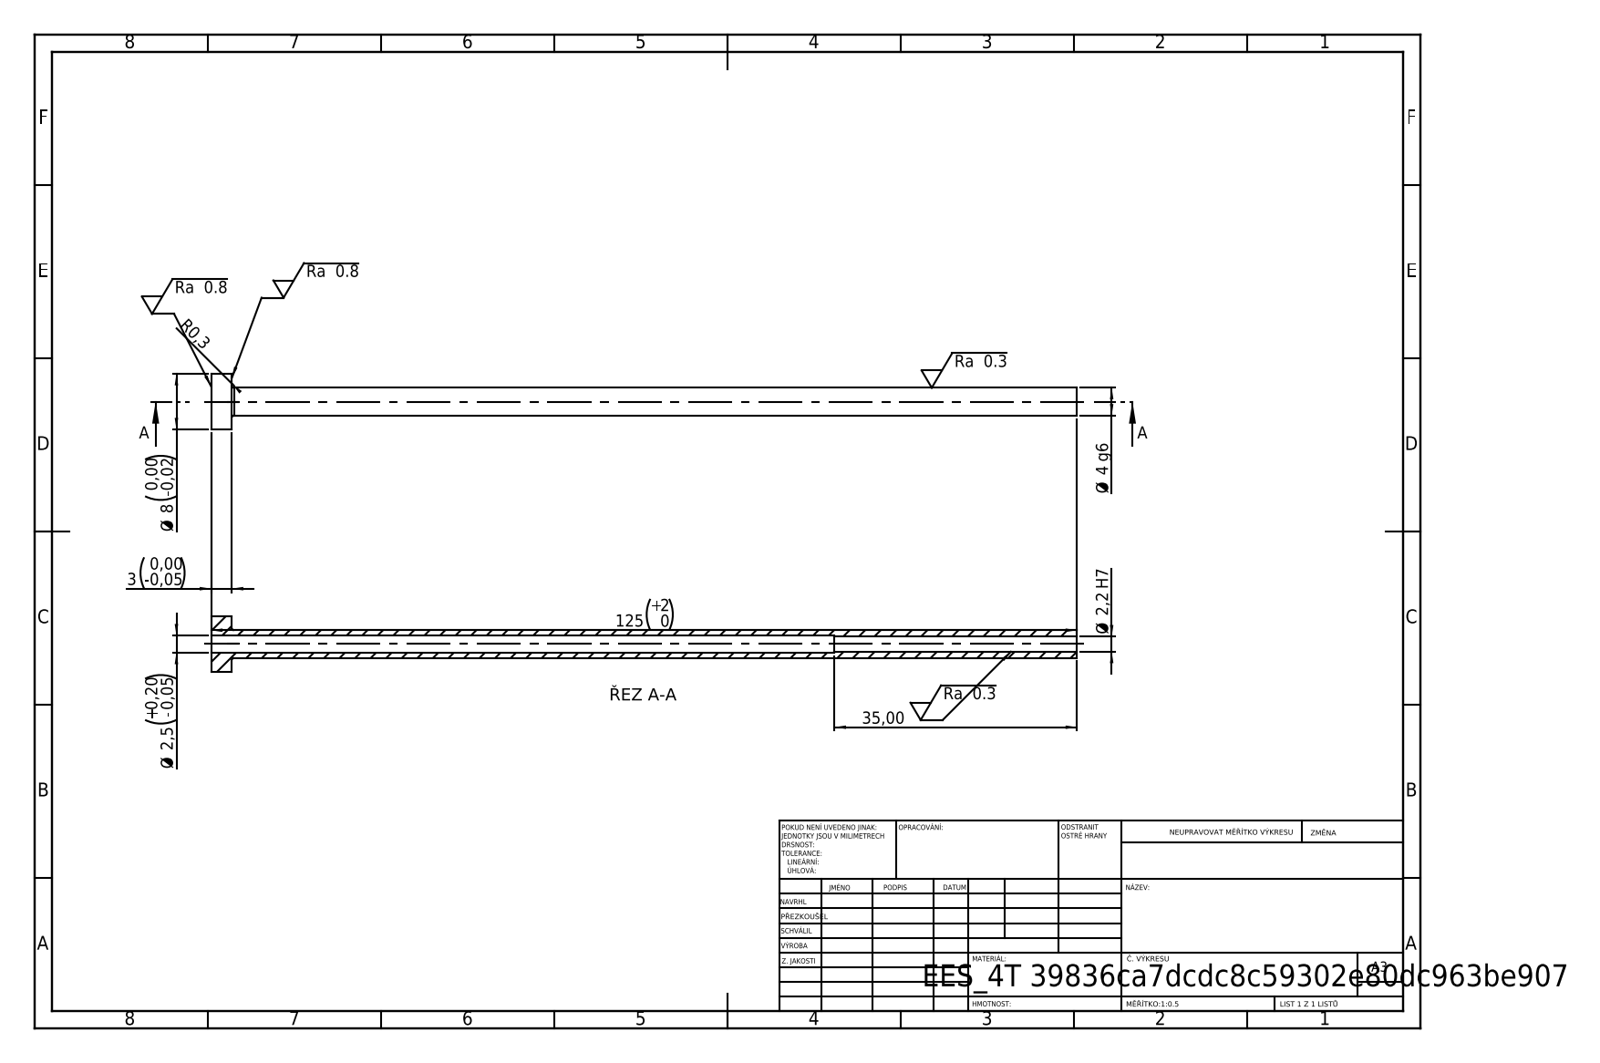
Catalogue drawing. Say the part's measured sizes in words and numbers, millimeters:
Its 3-D file was written by "SolidWorks 2019 (CONFIG_CONTROL_DESIGN)". It is 1 solid with 14 faces: 4 planar, 8 cylindrical and 2 other. Overall it measures 125 by 8 by 8 millimeters. Its volume is 1 109 cubic millimeters and its surface area 2 649 square millimeters. Round holes: 1 of diameter 2.2, 1 of diameter 2.5. Round bosses or shafts: 1 of diameter 8, 1 of diameter 4. The main face-to-face distances are 3, 125, 122, 90, 87, 35.
